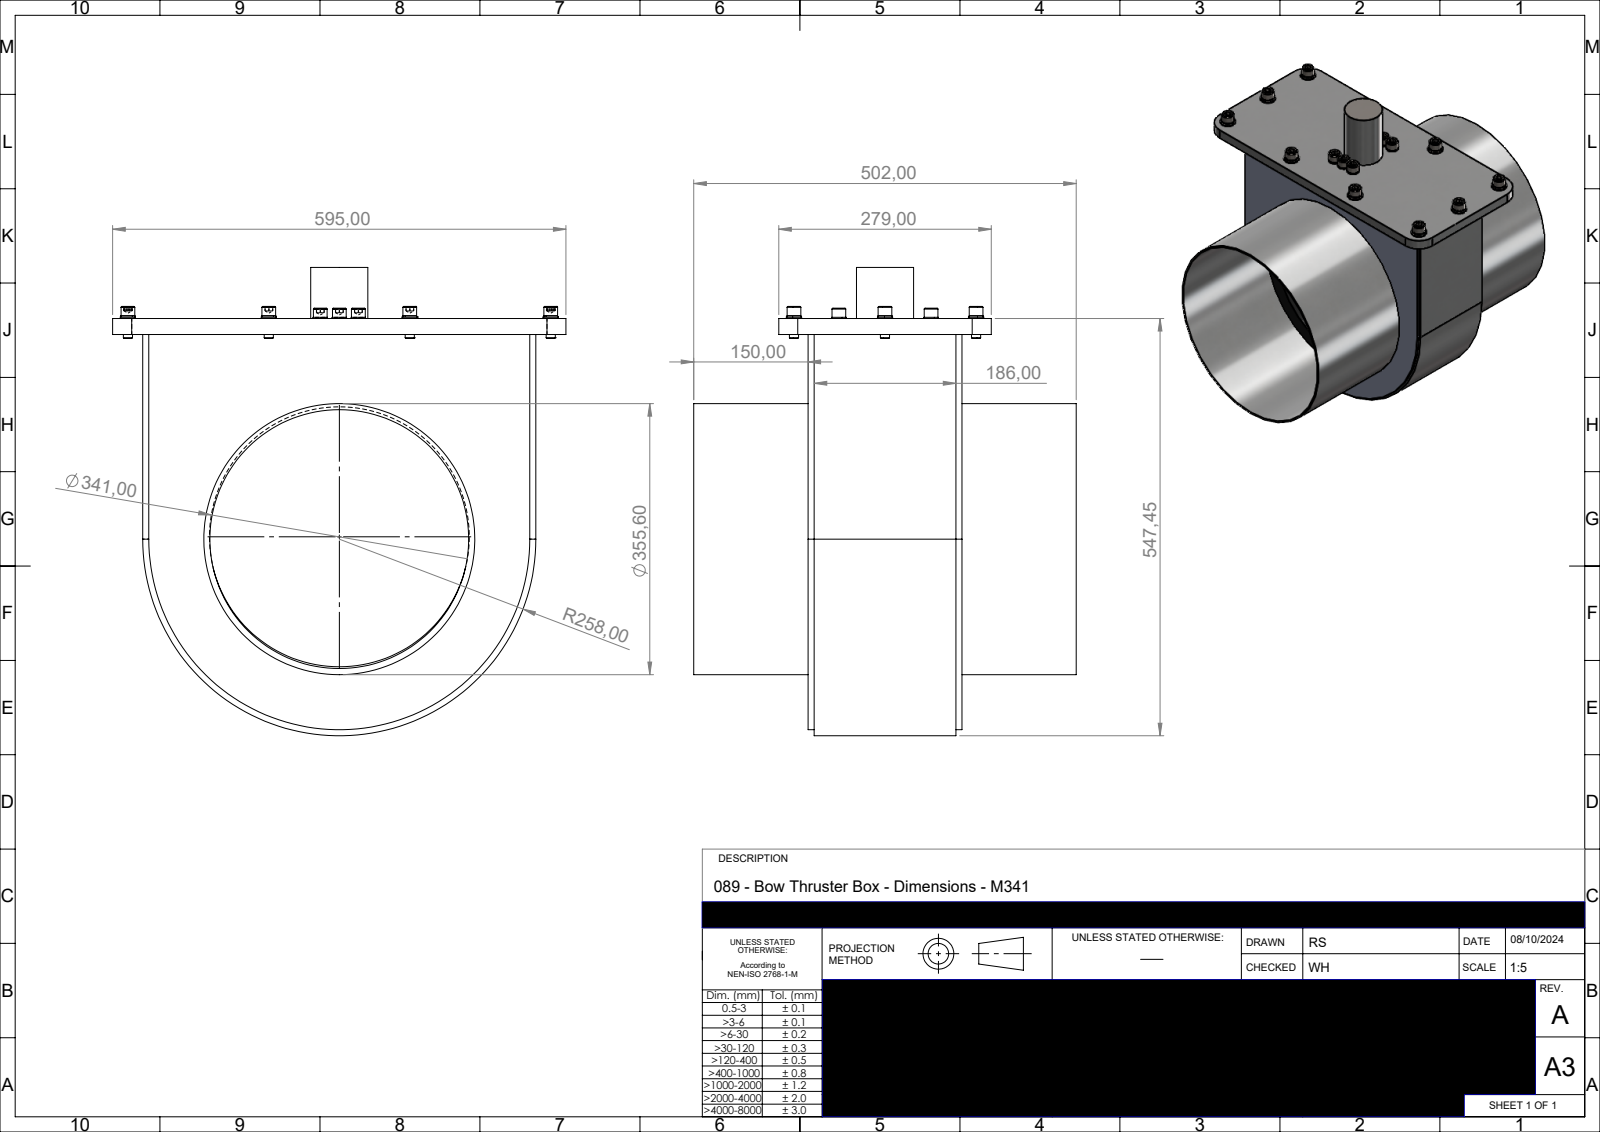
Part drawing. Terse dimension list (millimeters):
name: P-089-030-rev-A-M341
written by: SolidWorks 2024 (AUTOMOTIVE_DESIGN)
unit: mm
bodies: 1 solid, 462 faces (307 planar, 87 cylindrical, 68 other)
size: 614.45 × 595 × 502
volume: 36 930 000 mm³; area: 1 751 000 mm²
holes: 6× ⌀12.7, 1× ⌀339.6, 1× ⌀341
bosses: 16× ⌀18, 16× ⌀12, 10× ⌀20, 10× ⌀18.1, 6× ⌀19, 1× ⌀355.6, 1× ⌀75
rounds: 4× R25, 1× R250, 1× R258
face distances: 202, 21, 516, 8, 38.5, 240.5, 46.5, 232.5, 194, 111.5
hole spacings: 25, 123.56, 121, 50, 130.92, 2.97
